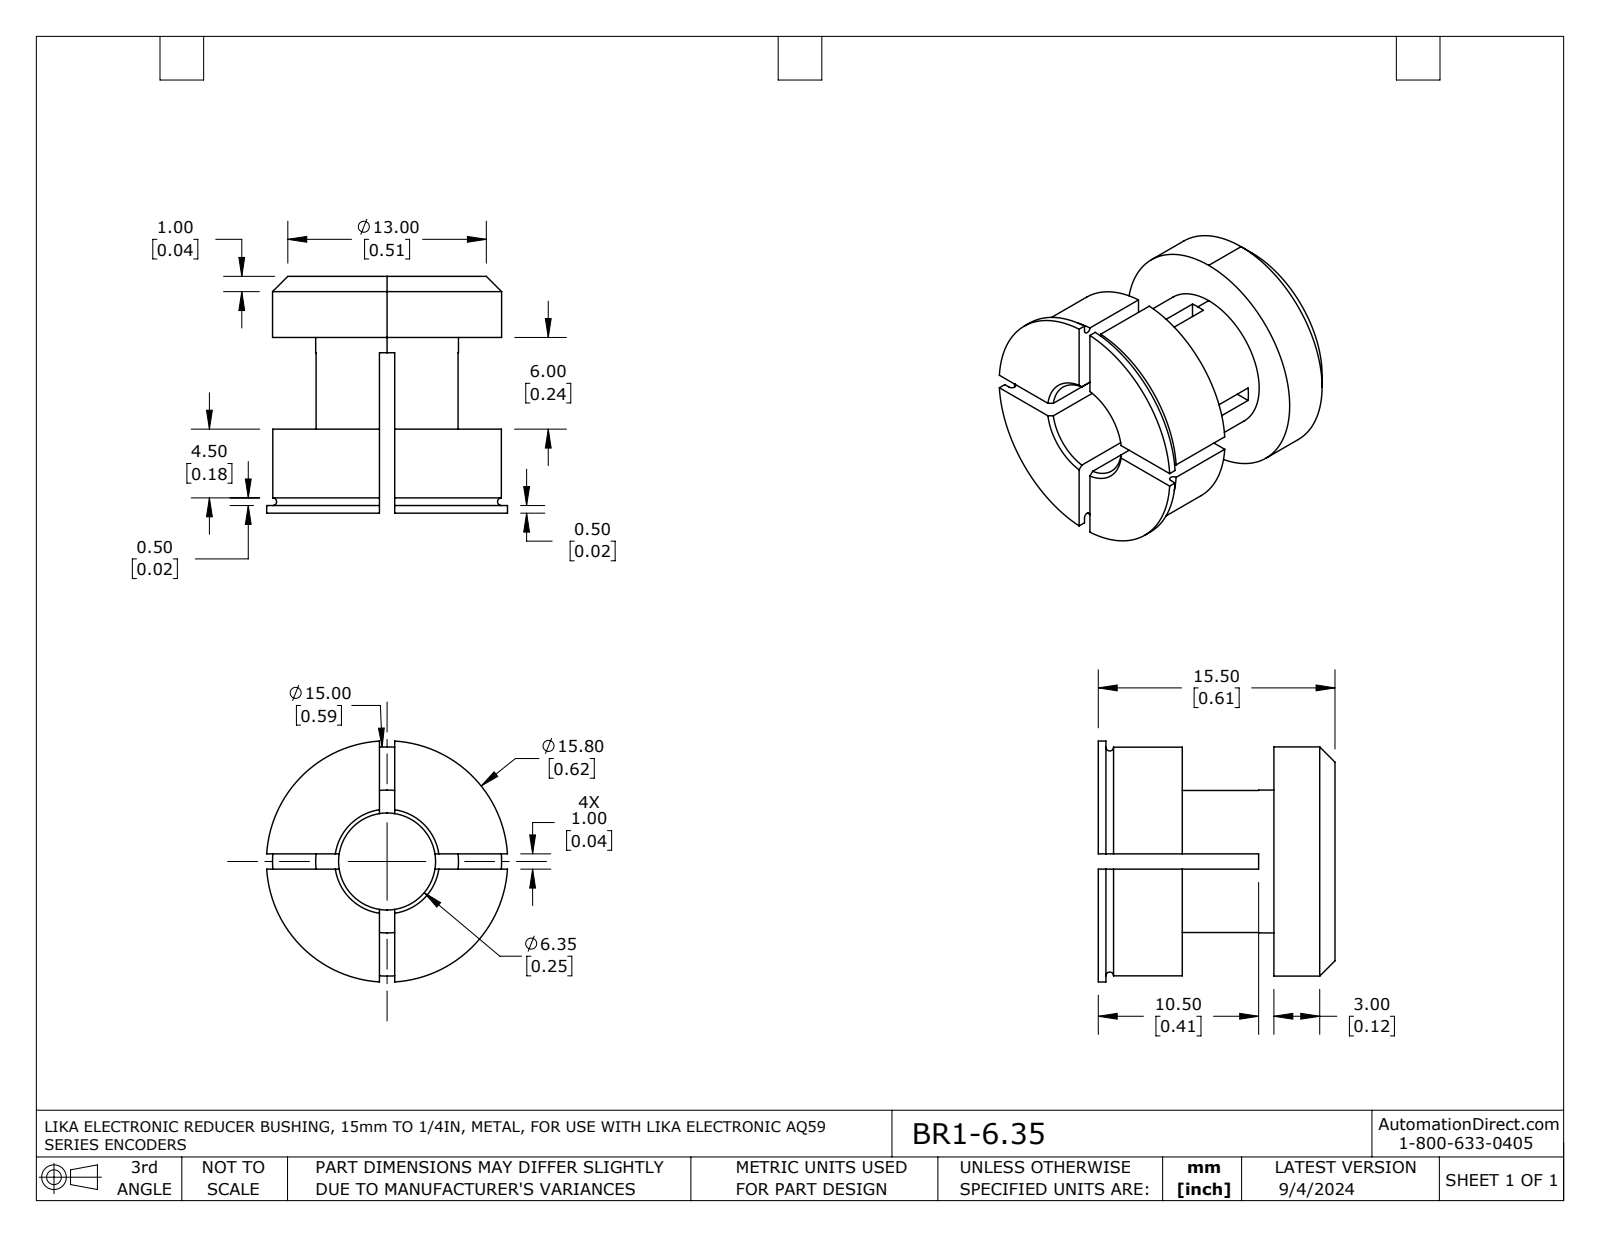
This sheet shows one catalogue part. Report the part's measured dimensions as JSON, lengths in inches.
{"part_name": "BR1-6.35", "step_written_by": "SolidWorks 2021 (CONFIG_CONTROL_DESIGN)", "units": "inches", "bodies": {"solids": 1, "faces": 54, "planar": 26, "cylindrical": 17, "other": 11}, "overall_size": [0.621, 0.621, 0.61], "volume_in3": 0.089, "surface_area_in2": 2.483, "round_holes": [[0.25, 1]], "round_bosses_or_shafts": [[0.622, 1], [0.591, 1], [0.368, 1]], "face_to_face_distances": [0.039, 0.453, 0.394, 0.157, 0.61, 0.236, 0.217, 0.197, 0.591, 0.433]}
